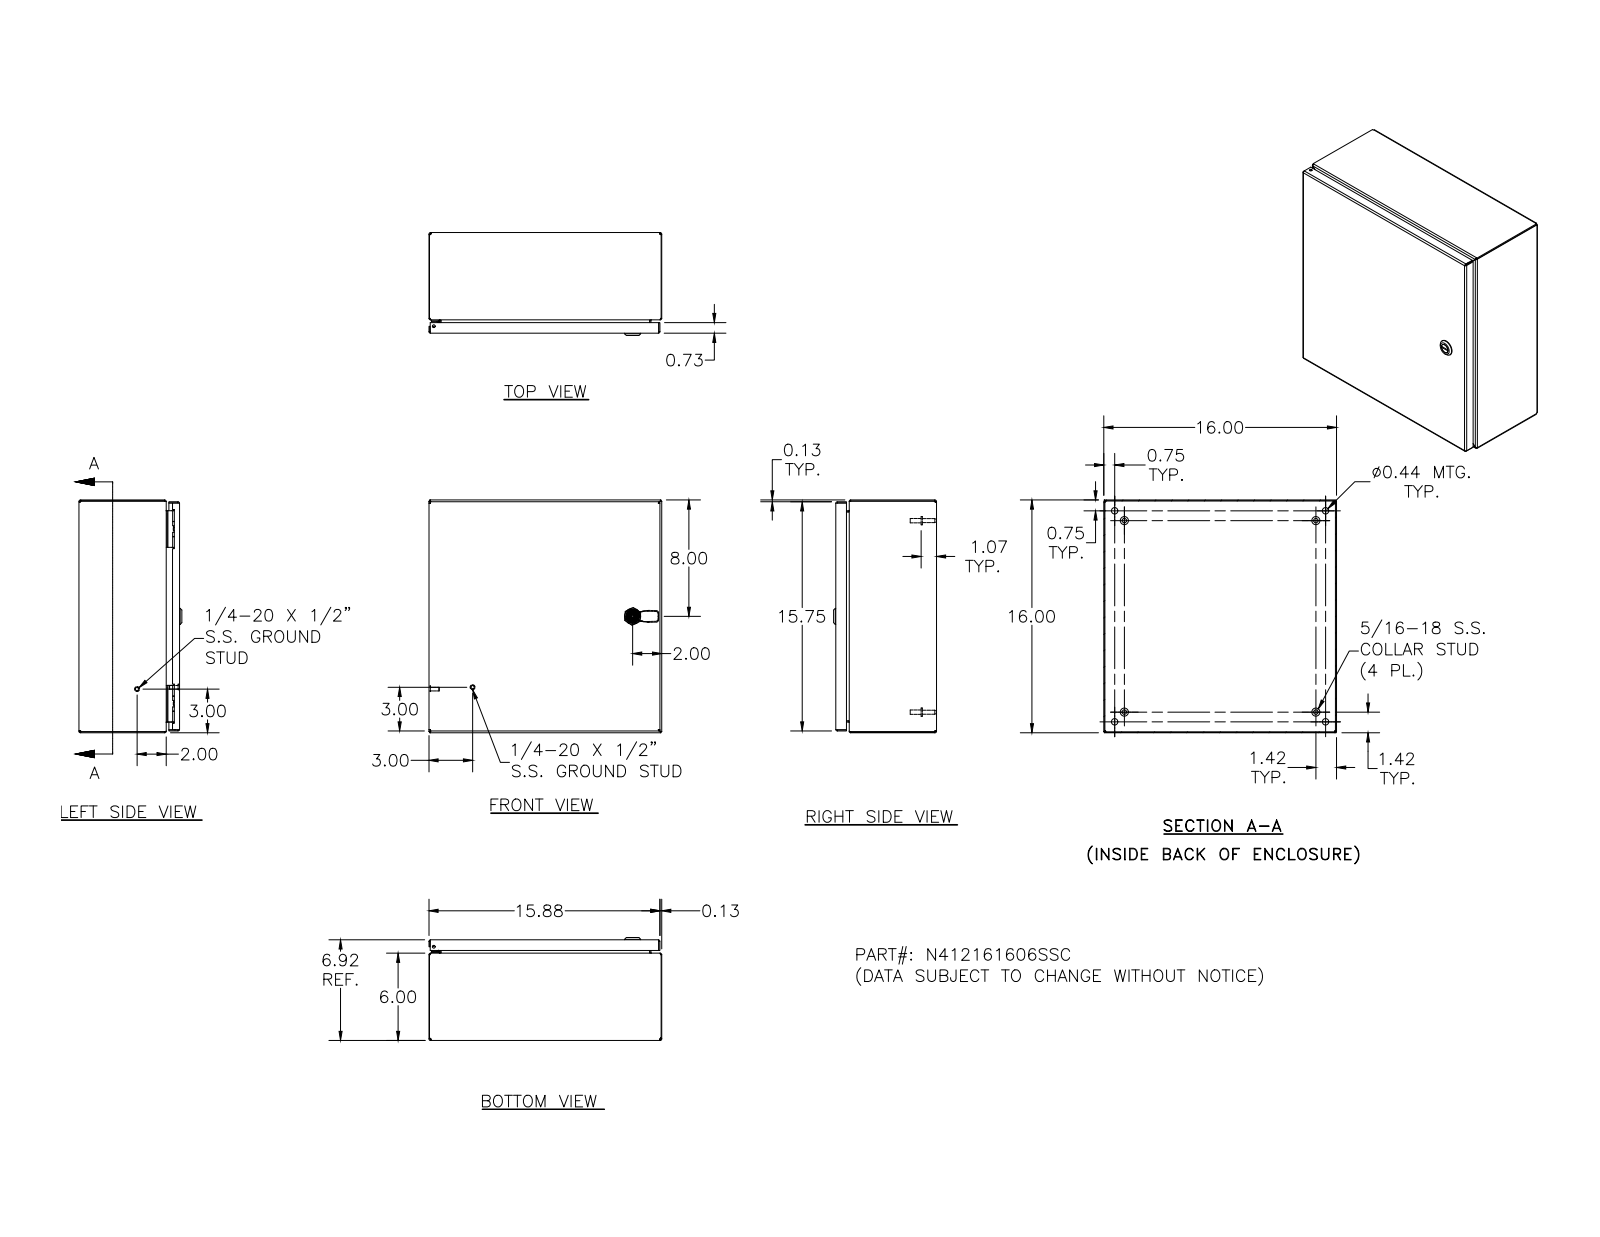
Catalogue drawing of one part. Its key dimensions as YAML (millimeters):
part_name: "N412161606SSC; N412161606SSCBKP; 388151; N4121616SSCLID (+8 more)"
step_written_by: "Autodesk Inventor 2011 (AUTOMOTIVE_DESIGN)"
units: millimeters
bodies: {solids: 34, faces: 1384, planar: 531, cylindrical: 509, other: 344}
overall_size: [406.4, 406.4, 179.7]
volume: 1251000
surface_area: 1341000
round_holes:
  - {diameter: 4.8, count: 5}
  - {diameter: 2.4, count: 4}
  - {diameter: 3.9, count: 4}
  - {diameter: 4.2, count: 4}
  - {diameter: 4.4, count: 4}
  - {diameter: 11.1, count: 4}
  - {diameter: 4, count: 2}
  - {diameter: 4.7, count: 1}
  - {diameter: 5, count: 1}
  - {diameter: 8, count: 1}
  - {diameter: 10, count: 1}
  - {diameter: 10.2, count: 1}
round_bosses_or_shafts:
  - {diameter: 6.4, count: 10}
  - {diameter: 14.3, count: 4}
  - {diameter: 9.1, count: 4}
  - {diameter: 8.1, count: 4}
  - {diameter: 7.6, count: 4}
  - {diameter: 7, count: 4}
  - {diameter: 6.5, count: 4}
  - {diameter: 4.2, count: 4}
partial_cylinders:
  - {radius: 0.8, count: 30}
  - {radius: 1.3, count: 26}
  - {radius: 2.7, count: 20}
  - {radius: 0.4, count: 18}
  - {radius: 3.2, count: 14}
  - {radius: 0.5, count: 9}
  - {radius: 0.8, count: 8}
  - {radius: 1.8, count: 8}
face_to_face_distances: [1.9, 173.8, 404.5, 171.9, 175.7, 406.4, 402.6, 150.5, 23.3, 18.8]
hole_center_spacings: [304.8, 0.4, 16.8, 368.3, 0.5, 12.7, 16.5, 16.6]
